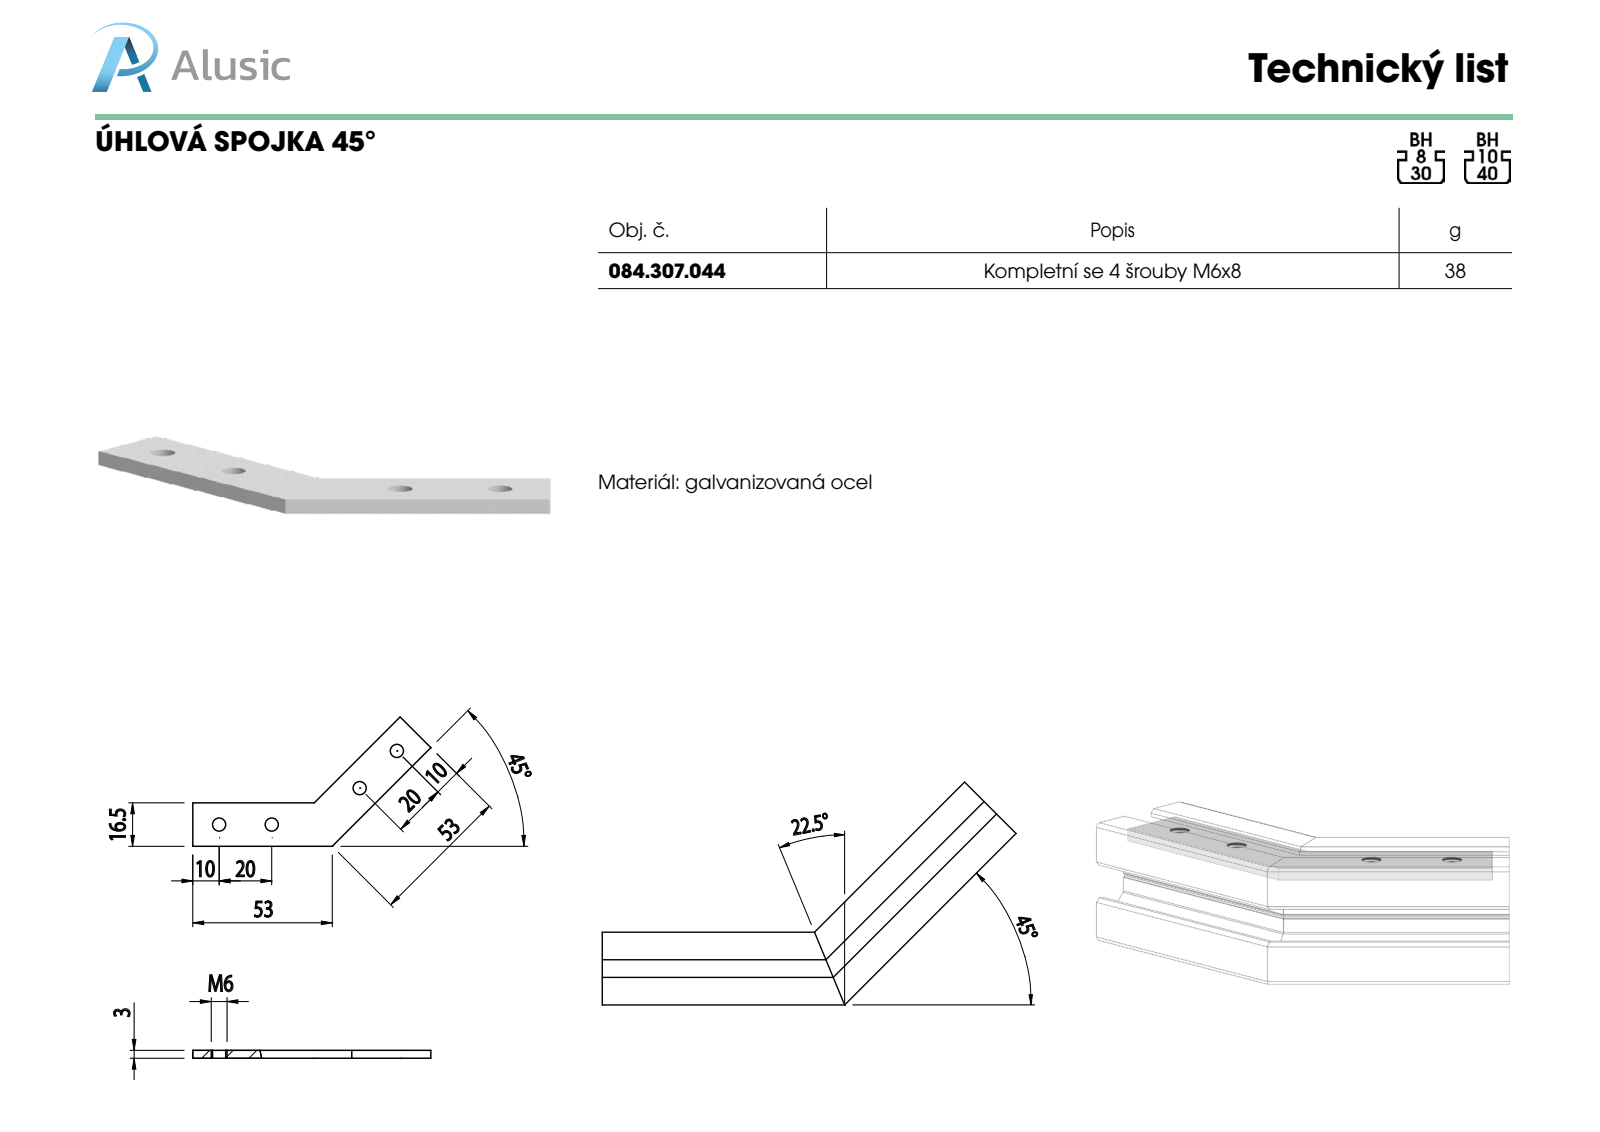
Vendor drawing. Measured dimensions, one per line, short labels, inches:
name: 084.307.044
written by: SolidWorks 2012 (CONFIG_CONTROL_DESIGN)
unit: in
bodies: 1 solid, 16 faces (8 planar, 8 cylindrical, 0 other)
size: 3.562 × 1.935 × 0.118
volume: 0.285 in³; area: 6.197 in²
holes: 4× ⌀0.197
face distances: 0.118, 0.65
hole spacings: 0.787, 1.425, 2.173, 2.173, 2.88
